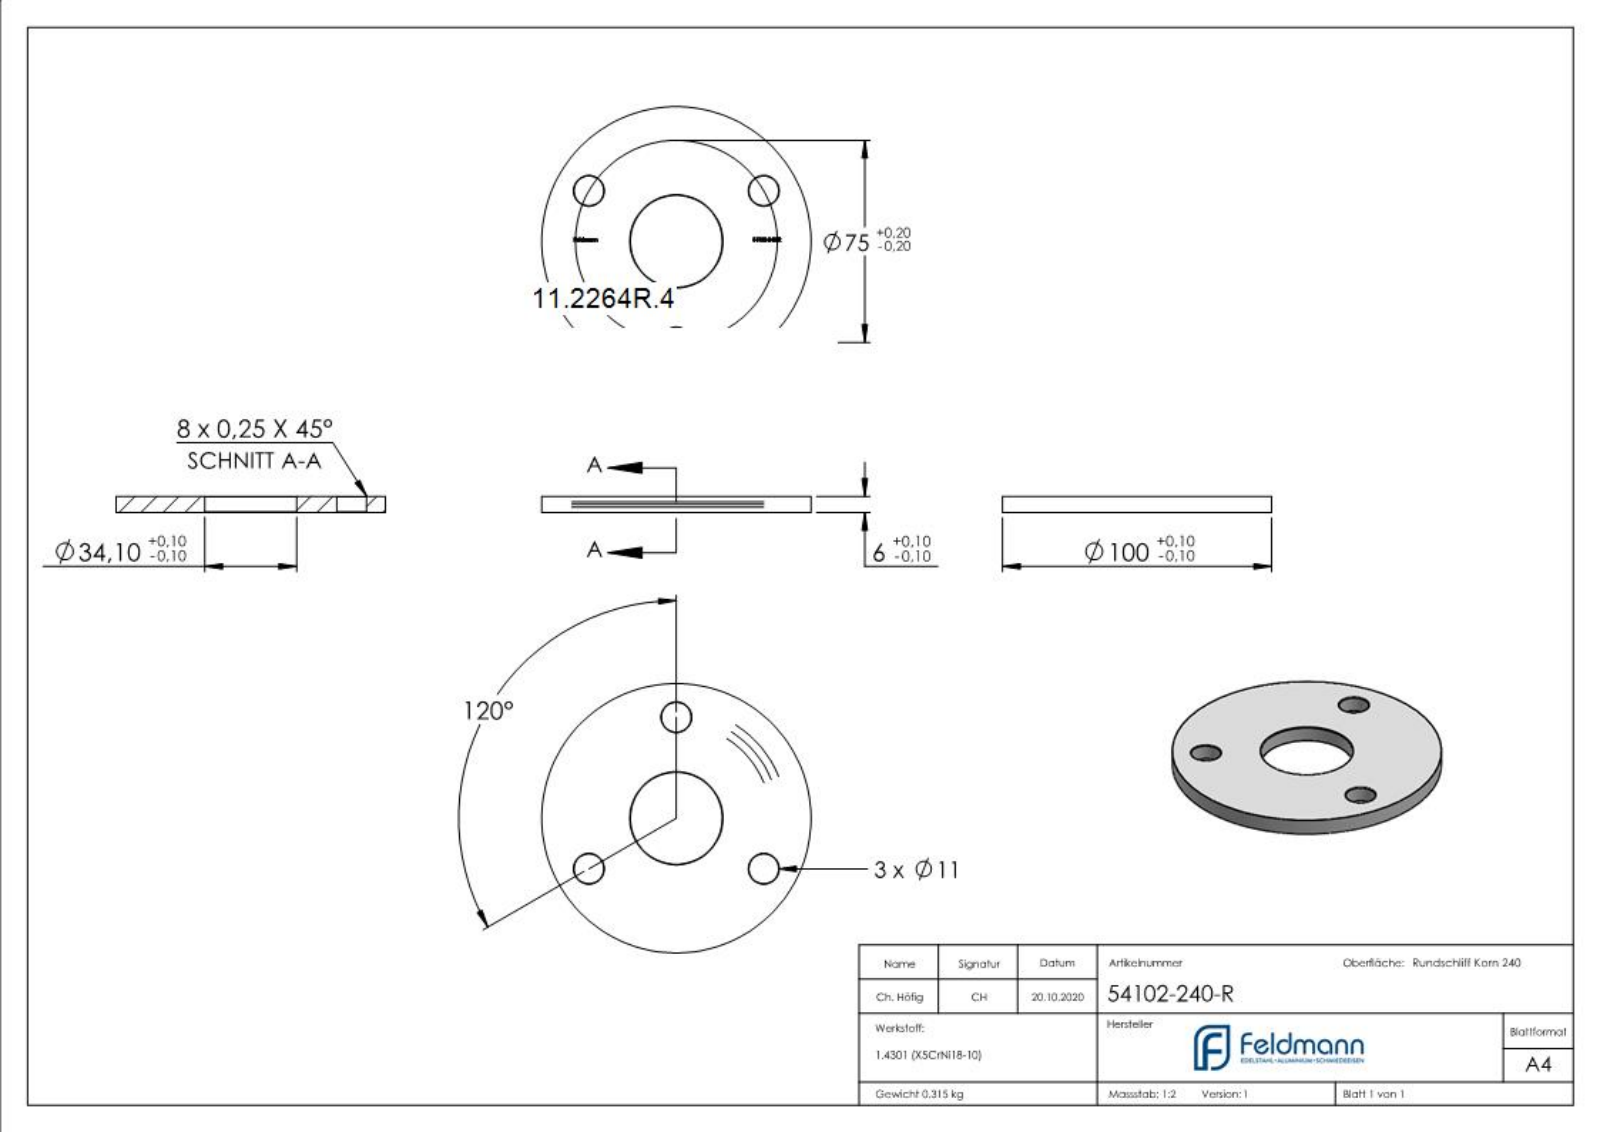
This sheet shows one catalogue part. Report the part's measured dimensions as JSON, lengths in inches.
{"part_name": "54102-240-R", "step_written_by": "SolidWorks 2018 (CONFIG_CONTROL_DESIGN)", "units": "inches", "bodies": {"solids": 1, "faces": 269, "planar": 152, "cylindrical": 10, "other": 107}, "overall_size": [3.937, 3.937, 0.236], "volume_in3": 2.436, "surface_area_in2": 25.44, "round_holes": [[0.433, 3], [1.343, 1]], "round_bosses_or_shafts": [[3.937, 1]], "face_to_face_distances": [0.236, 0.232, 0.017, 0.035, 0.047, 0.08, 2.907, 2.987, 0.023, 2.71], "hole_center_spacings": [1.476, 2.557, 2.557]}
